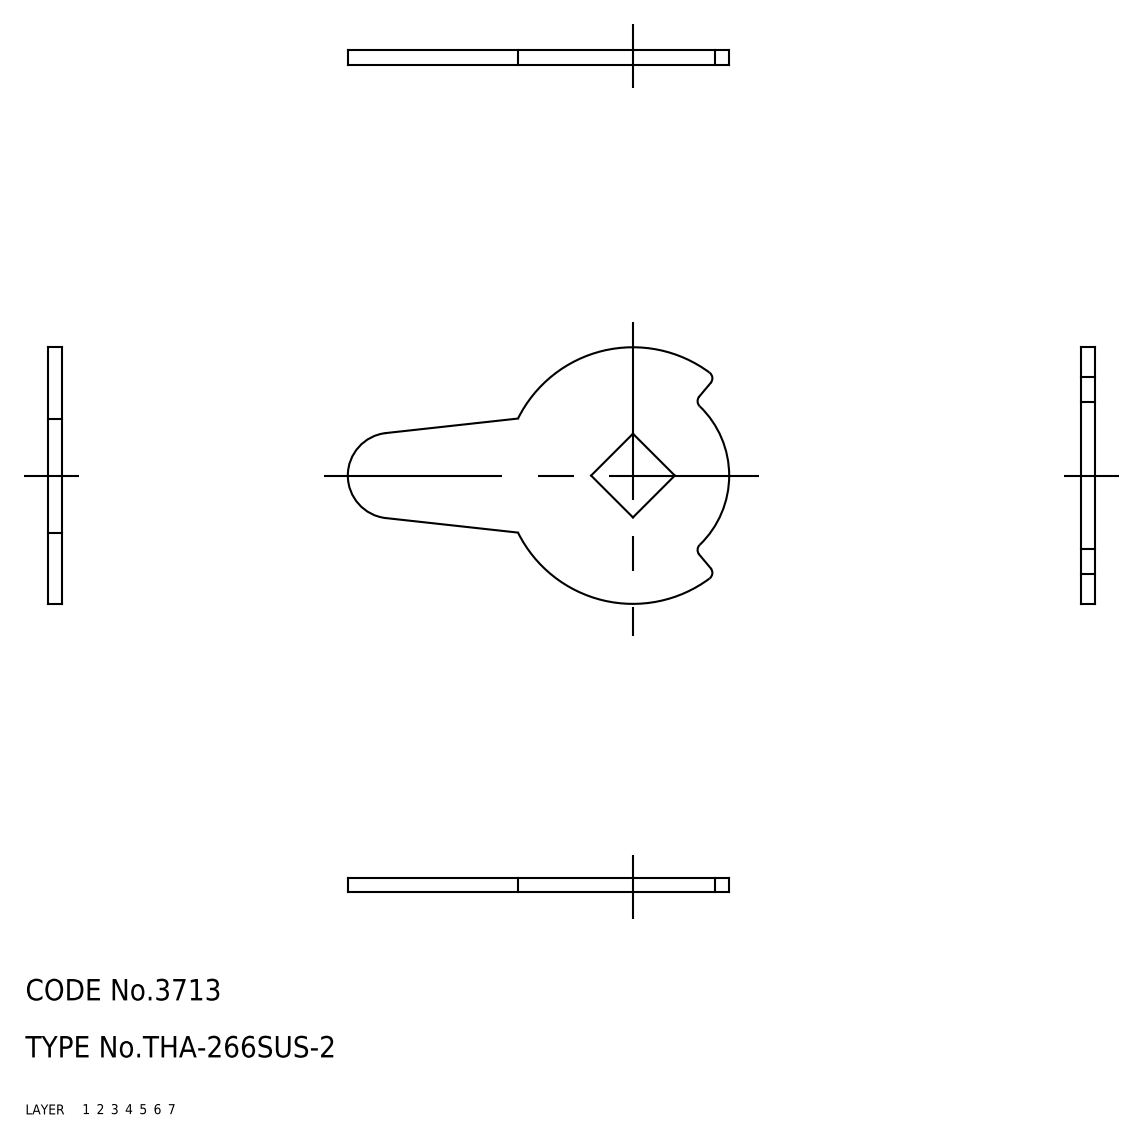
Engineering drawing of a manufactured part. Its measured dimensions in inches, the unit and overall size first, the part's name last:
Units: inches
Overall size (bounding box): 2.106 × 1.417 × 0.079
Volume: 0.136 in³ · Surface area: 4.019 in²
Bodies: 1 solid, 18 faces (0 planar, 0 cylindrical, 18 other)
Part name (STEP PRODUCT): cam
STEP written by: CADfix (AUTOMOTIVE_DESIGN)
